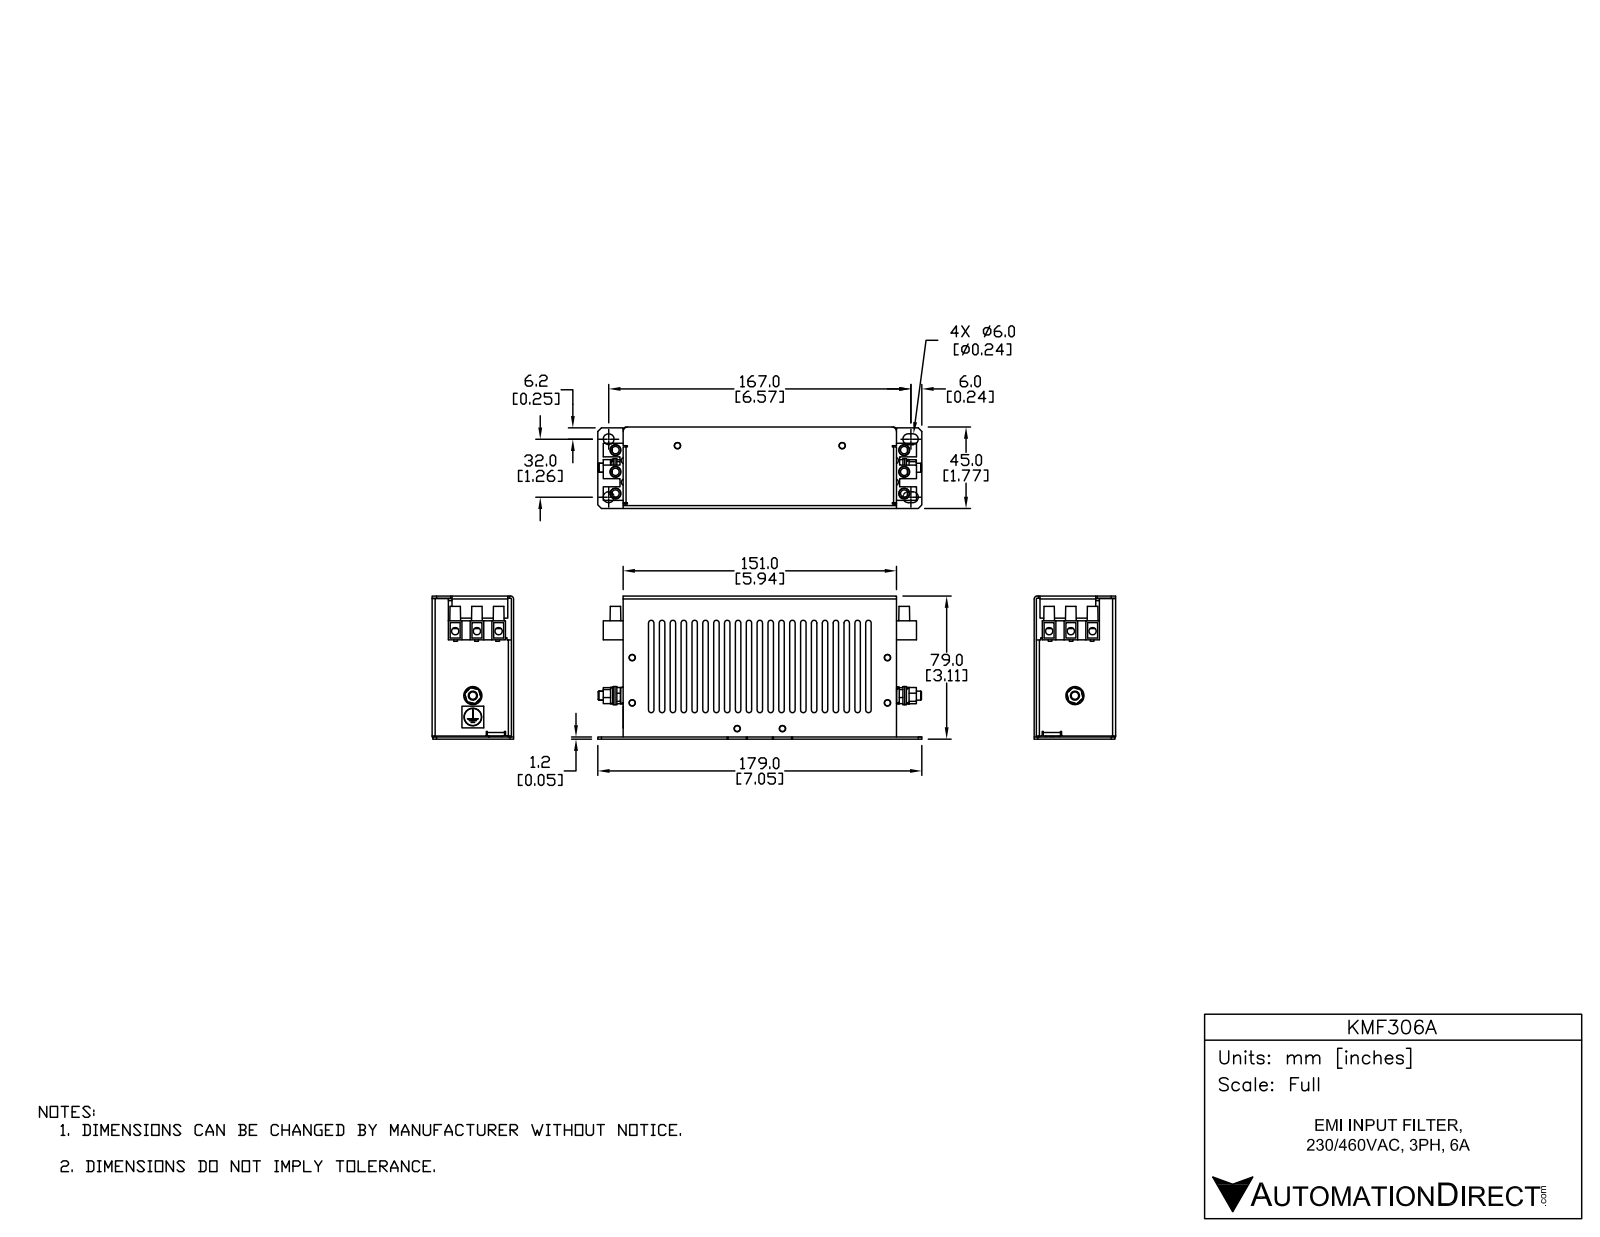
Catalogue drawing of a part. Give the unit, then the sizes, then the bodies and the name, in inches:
Units: inches
Overall size (bounding box): 7.047 × 3.11 × 1.772
Round holes (diameter × count): ⌀0.161 ×12, ⌀0.138 ×10, ⌀0.13 ×8, ⌀0.142 ×4, ⌀0.157 ×3, ⌀0.126 ×2, ⌀0.154 ×2, ⌀0.236 ×2, ⌀0.051 ×1, ⌀0.165 ×1, ⌀0.205 ×1, ⌀0.383 ×1
Round bosses / shafts (diameter × count): ⌀0.394 ×1, ⌀0.373 ×1, ⌀0.307 ×1, ⌀0.268 ×1, ⌀0.262 ×1, ⌀0.234 ×1, ⌀0.213 ×1, ⌀0.197 ×1
Partial cylindrical surfaces — rounded edges, fillets, slot ends (radius × count): R0.059 ×42, R0.02 ×17, R0.118 ×8, R0.067 ×5, R0.029 ×4, R0.076 ×4, R0.016 ×3, R0.063 ×3
Main face-to-face distances: 0.047, 1.724, 3.063, 1.677, 1.772, 3.11, 3.016, 5.898, 3.008, 0.055
Hole centre spacings: 0.472, 5.905, 0.3, 0.315, 0.615, 5.886, 0.394, 0.945
Volume: 3.794 in³ · Surface area: 165 in²
Bodies: 25 solids, 1428 faces (1018 planar, 352 cylindrical, 58 other)
Part name (STEP PRODUCT): KMF306A
STEP written by: SolidWorks 2017 (AUTOMOTIVE_DESIGN)
